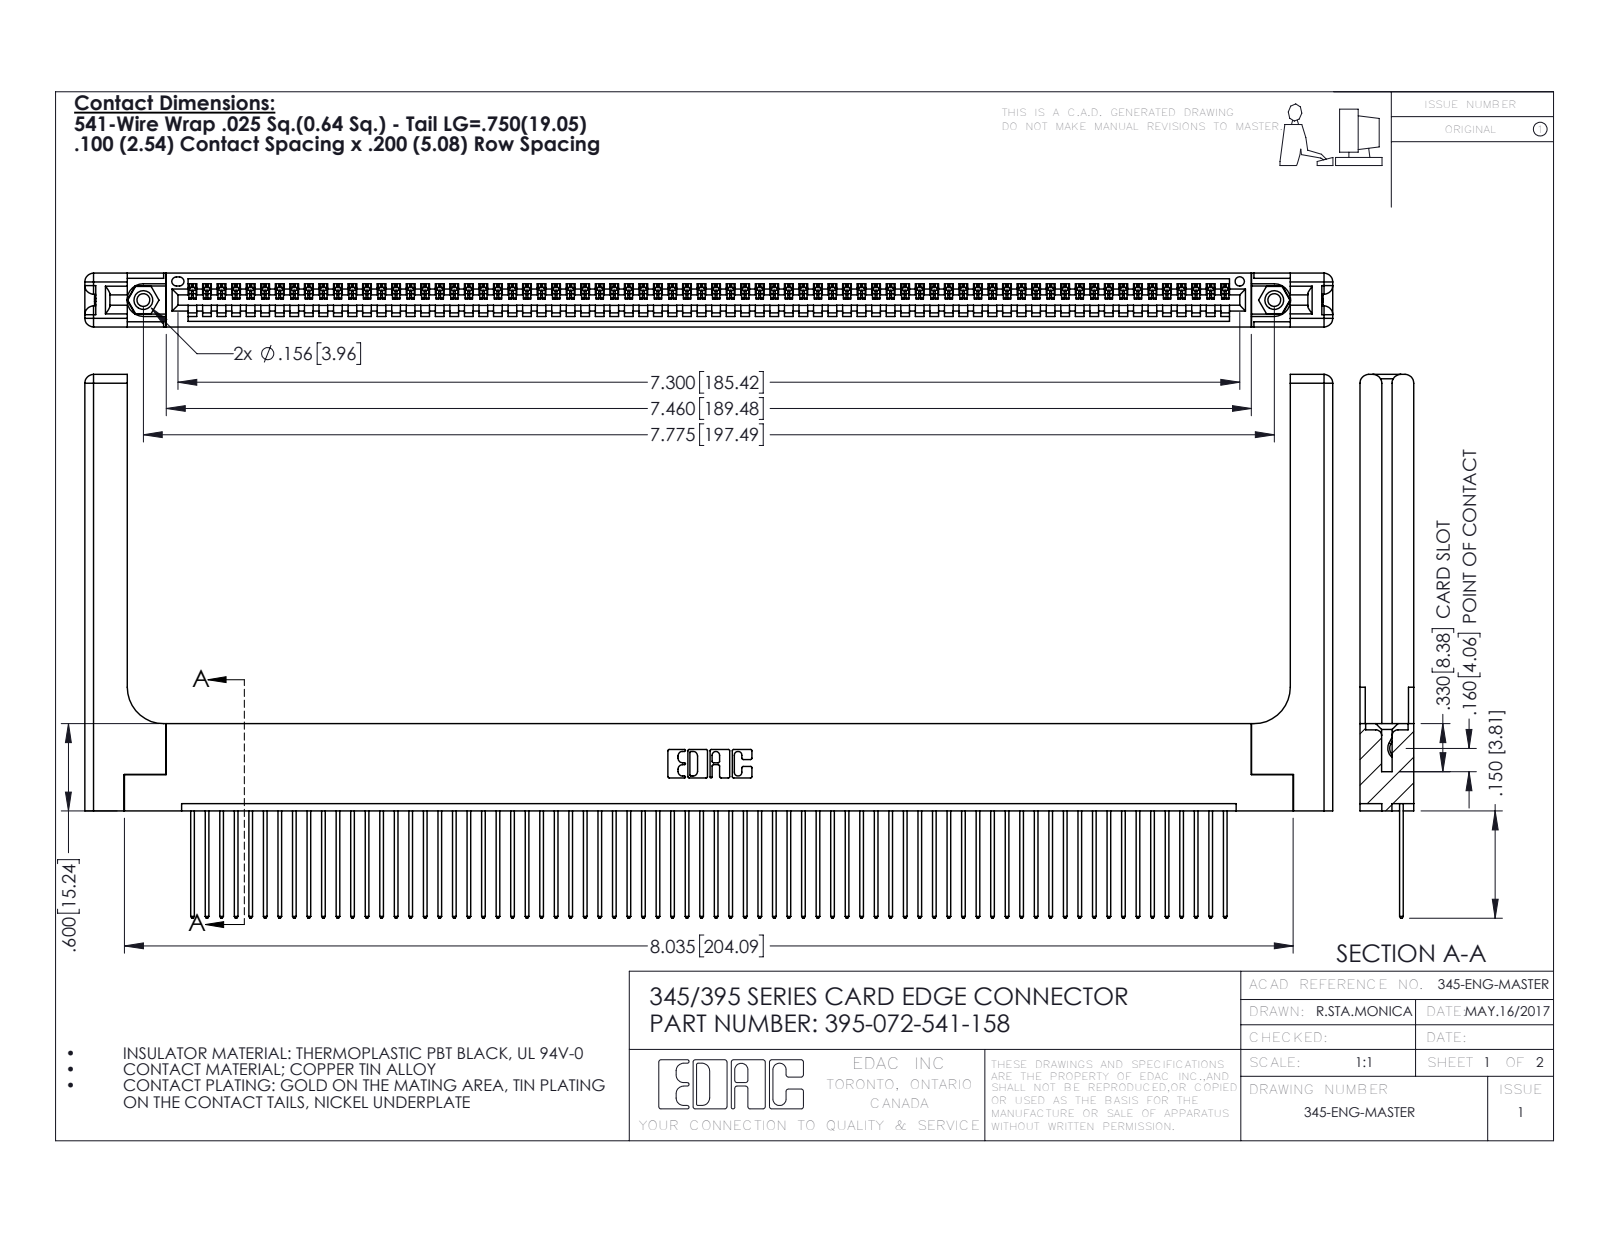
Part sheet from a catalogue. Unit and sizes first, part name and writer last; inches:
Units: inches
Overall size (bounding box): 8.579 × 3.737 × 0.37
Round holes (diameter × count): ⌀0.089 ×2, ⌀0.125 ×2, ⌀0.156 ×2, ⌀0.064 ×1
Round bosses / shafts (diameter × count): ⌀0.155 ×2
Partial cylindrical surfaces — rounded edges, fillets, slot ends (radius × count): R0.006 ×144, R0.01 ×144, R0.01 ×22, R0.06 ×16, R0.007 ×6, R0.031 ×6, R0.026 ×3, R0.03 ×2
Main face-to-face distances: 0.072, 0.298, 0.37, 0.098, 0.272, 0.025, 0.2, 0.225, 0.148, 0.15
Hole centre spacings: 0.27, 7.539, 7.775
Volume: 1.812 in³ · Surface area: 54.65 in²
Bodies: 77 solids, 4558 faces (3108 planar, 1390 cylindrical, 60 other)
Part name (STEP PRODUCT): 395-072-541-158; 345-292-001_345-293-141; 345-220-058_345-220-058; 345 Part_Flush Mounting Lugs - 0.156 Dia-TH (+1 more)
STEP written by: SolidWorks 2016 (CONFIG_CONTROL_DESIGN)
